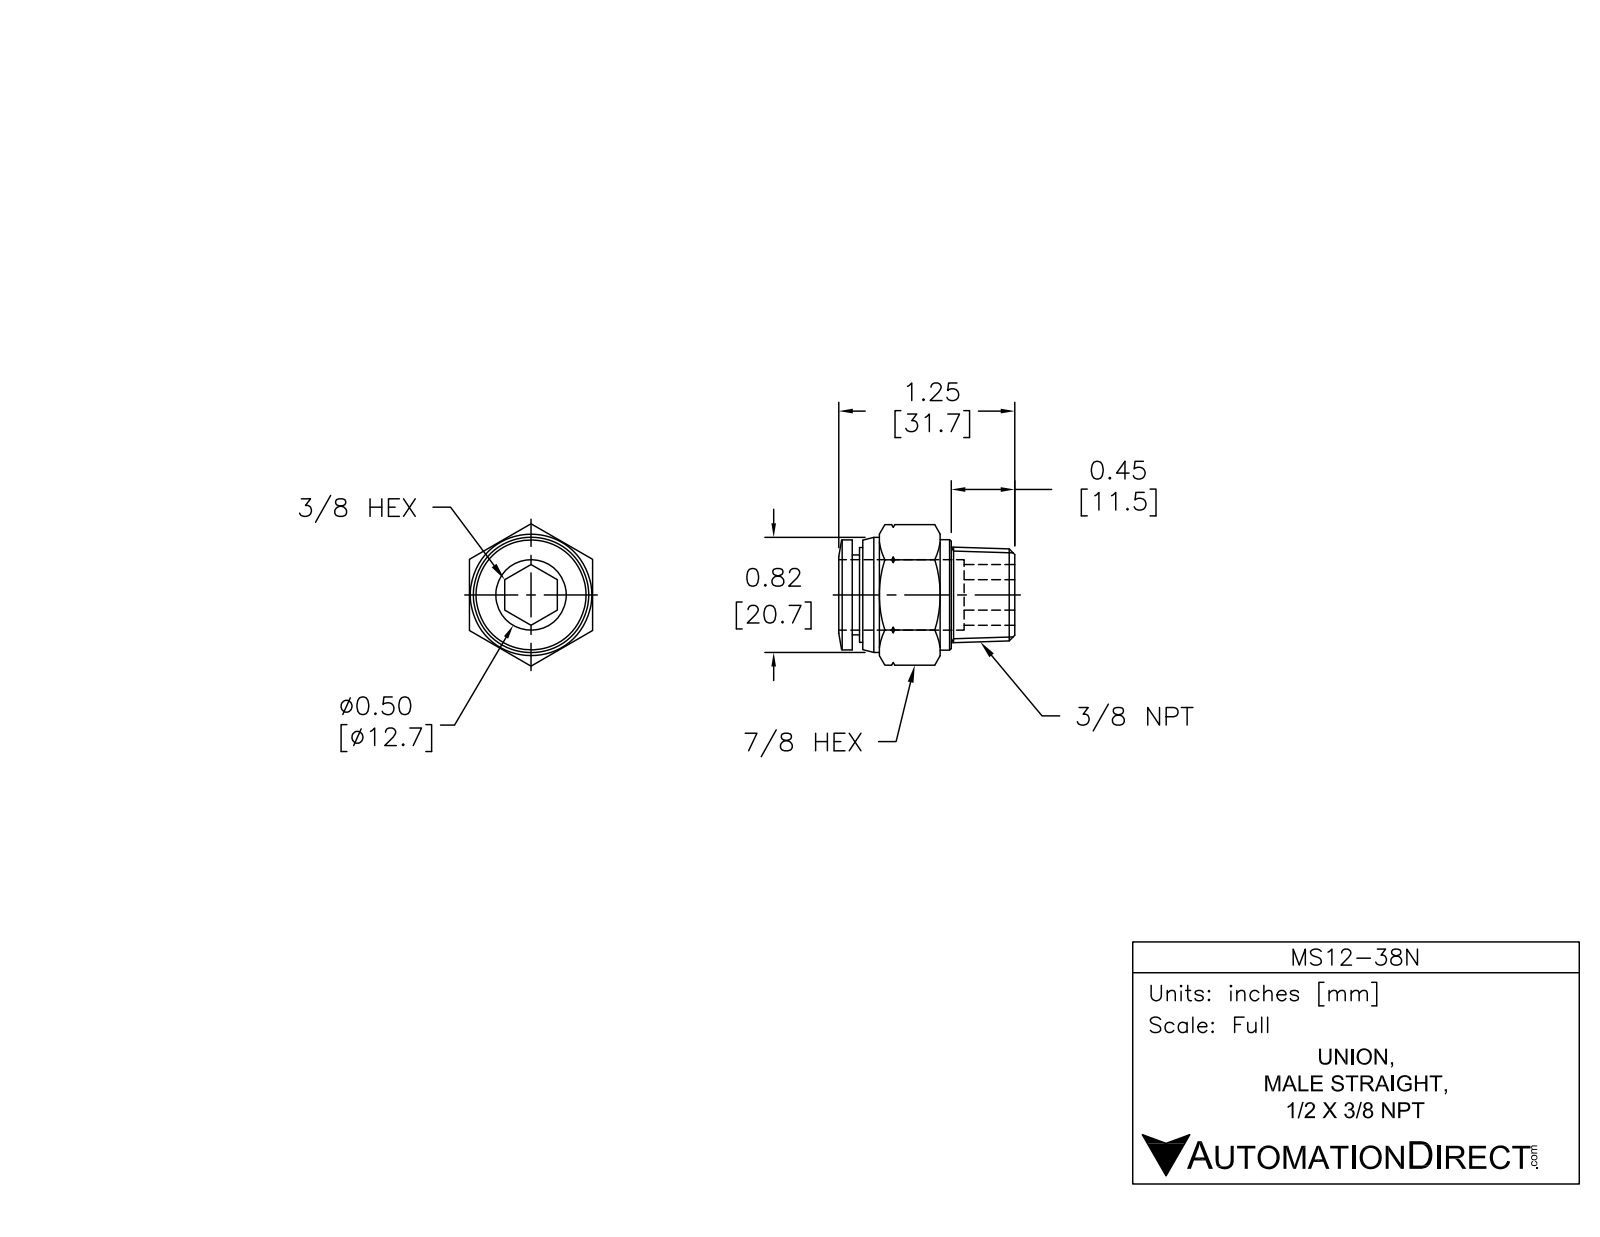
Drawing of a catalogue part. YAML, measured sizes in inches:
part_name: "PC1-2--N03"
step_written_by: "Autodesk Inventor 2008 (AUTOMOTIVE_DESIGN)"
units: inches
bodies: {solids: 1, faces: 53, planar: 14, cylindrical: 7, other: 32}
overall_size: [1.254, 1, 0.866]
volume: 0.378
surface_area: 6.25
round_holes:
  - {diameter: 0.374, count: 1}
  - {diameter: 0.51, count: 1}
round_bosses_or_shafts:
  - {diameter: 0.819, count: 1}
  - {diameter: 0.787, count: 1}
  - {diameter: 0.783, count: 1}
  - {diameter: 0.675, count: 1}
  - {diameter: 0.569, count: 1}
face_to_face_distances: [0.866, 1.157, 1.083, 0.075, 1.106, 0.024, 0.051, 0.531, 0.551, 0.575]
